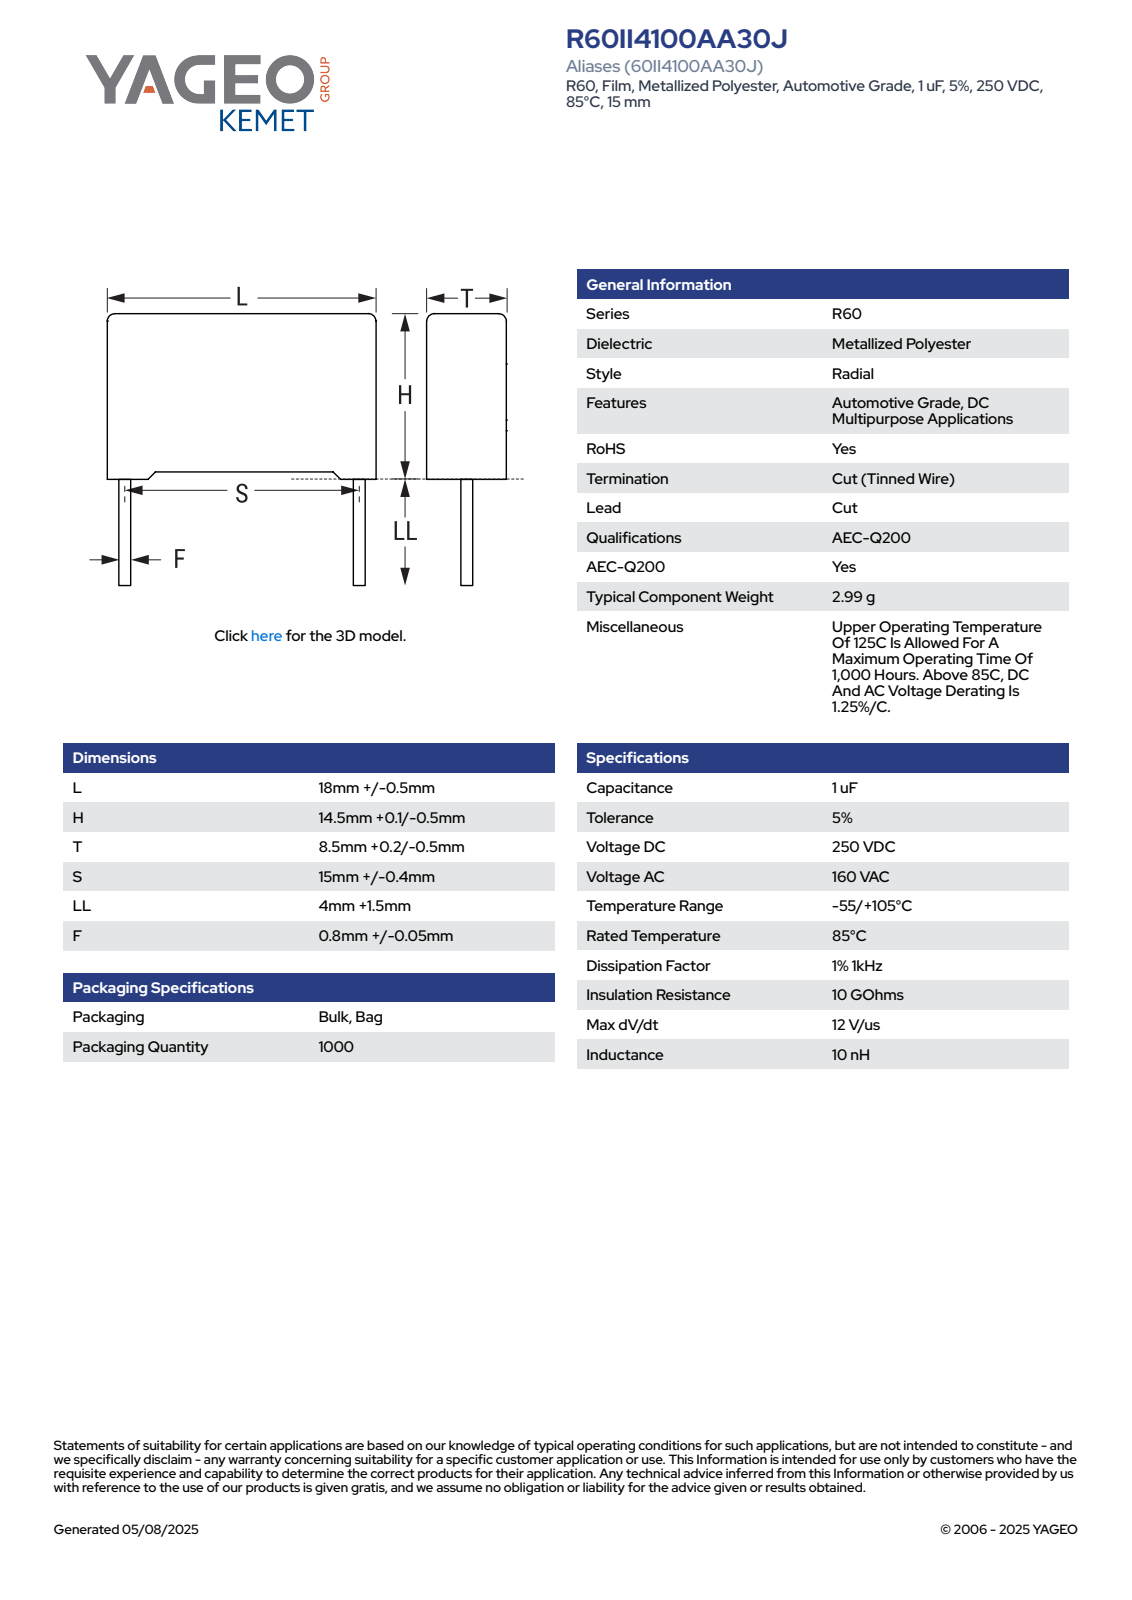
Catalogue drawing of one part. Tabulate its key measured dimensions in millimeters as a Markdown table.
| quantity | value |
| --- | --- |
| part name | CFR_RB2_18X14.5X8.5_L18.5H14.6T8.7S15LL5.5F0.85 |
| STEP written by | SolidWorks 2021 (AUTOMOTIVE_DESIGN) |
| units | millimeters |
| bodies | 4 solids, 85 faces (77 planar, 8 cylindrical, 0 other) |
| overall size | 20.1 × 18.5 × 8.71 |
| volume | 2 250 mm³ |
| surface area | 1 178 mm² |
| round bosses / shafts (diameter × count) | 0.85 × 2 |
| partial cylindrical surfaces (radius × count) | 0.5 × 4 |
| main face-to-face distances | 8.7, 13.85, 18.5, 0.62, 0.75, 14.6, 8.08, 0.5, 14.1, 17.88 |
